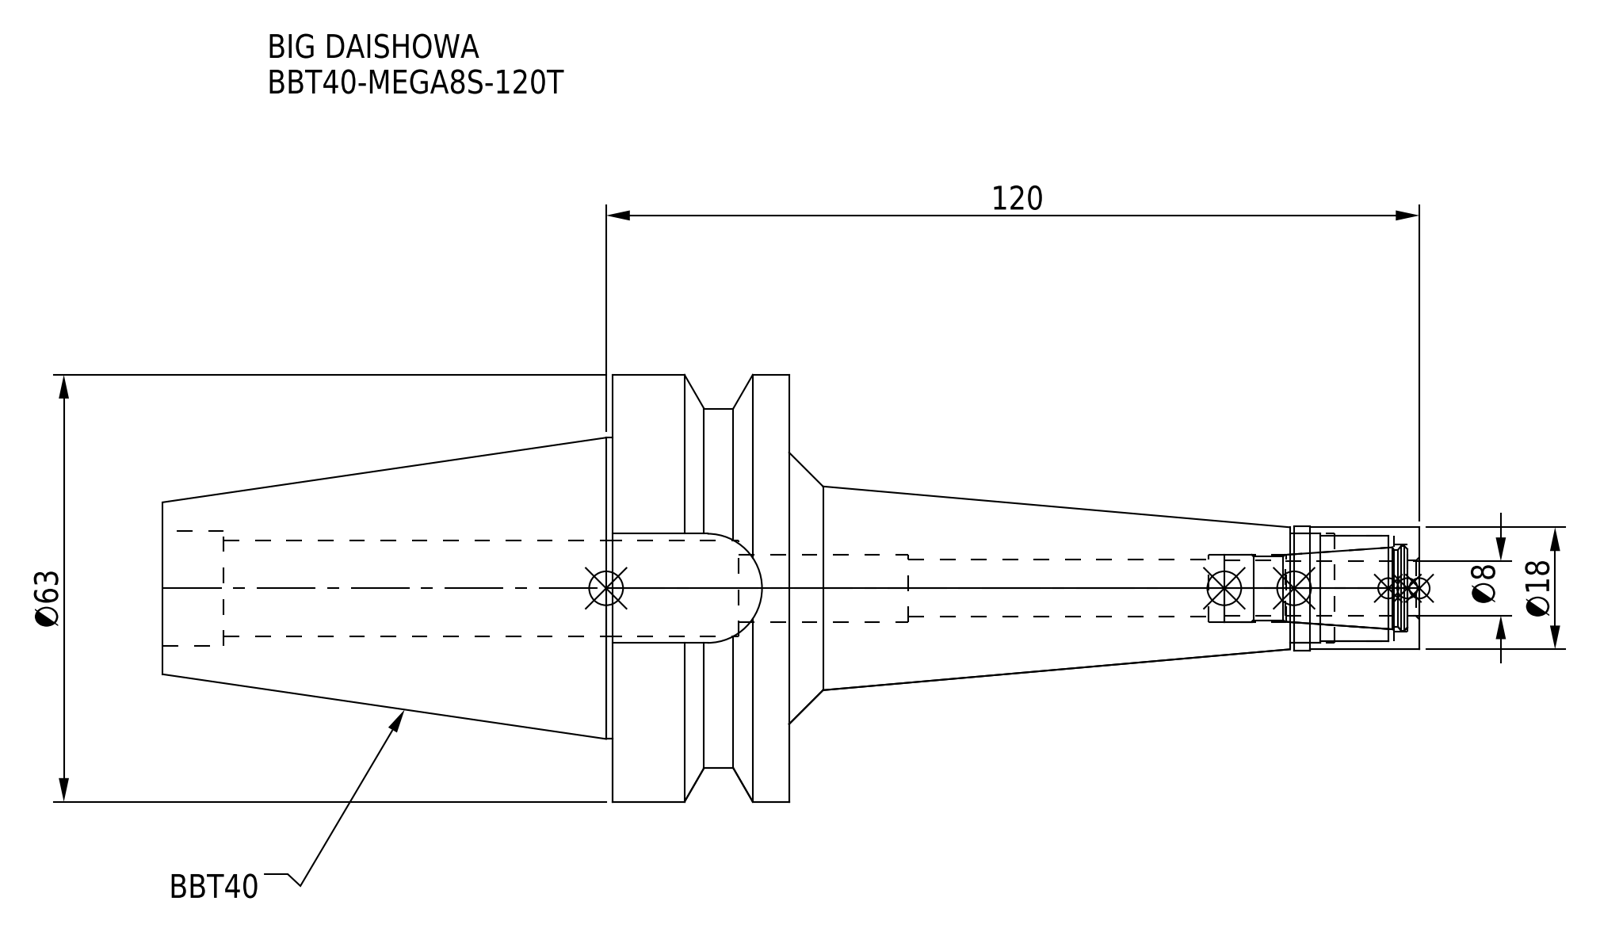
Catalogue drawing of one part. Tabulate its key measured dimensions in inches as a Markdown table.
| quantity | value |
| --- | --- |
| part name | BBT40MS08120T-080_ASM.stp; BBT40-MEGA8S-120T; MGN8S_1.stp; BBT40-MEGA8S-120T_1.stp (+3 more) |
| STEP written by | SolidWorks 2019 (CONFIG_CONTROL_DESIGN) |
| units | inches |
| bodies | 2 solids, 74 faces (22 planar, 38 cylindrical, 14 other) |
| overall size | 7.299 × 2.48 × 2.48 |
| volume | 9.51 in³ |
| surface area | 51.76 in² |
| round holes (diameter × count) | 0.323 × 1, 0.331 × 1, 0.39 × 1, 0.394 × 1, 0.508 × 1, 0.559 × 1, 0.614 × 1, 0.634 × 1, 0.669 × 1 |
| round bosses / shafts (diameter × count) | 2.48 × 1, 2.087 × 1, 1.75 × 1, 0.72 × 1, 0.709 × 1 |
| partial cylindrical surfaces (radius × count) | 0.317 × 1 |
| main face-to-face distances | 1.024, 1.772, 3.638, 2.614, 0.634, 3.661, 4.685, 7.299, 0.732, 3.953 |
